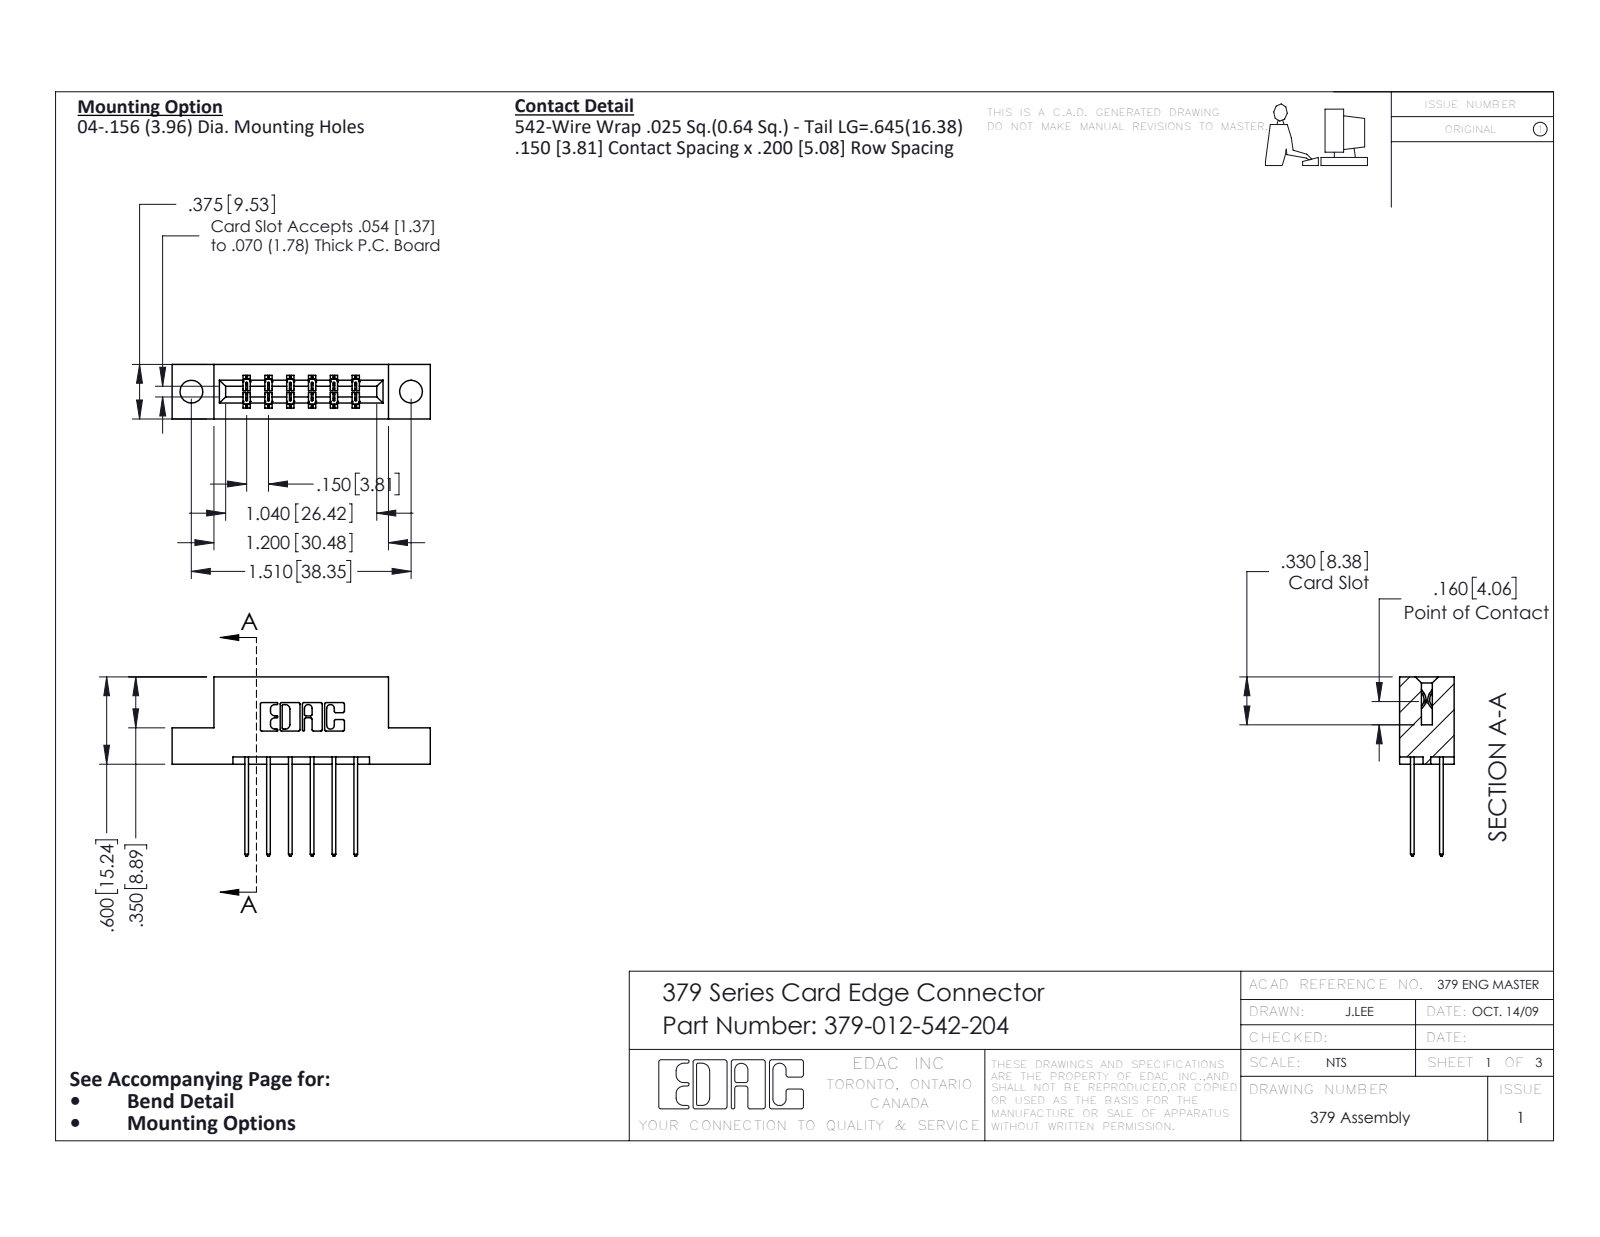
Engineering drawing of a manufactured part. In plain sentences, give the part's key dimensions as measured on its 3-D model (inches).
The part is named "379 Part_Flush - .156 Dia - TH; 379-012-542-204; 345-292-001_345-293-142". Its 3-D file was written by "SolidWorks 2016 (CONFIG_CONTROL_DESIGN)". It is 13 solids with 738 faces: 502 planar, 236 cylindrical and 0 other. Overall it measures 1.775 by 1.232 by 0.375 inches. Its volume is 0.263 cubic inches and its surface area 7.118 square inches. Round holes: 2 of diameter 0.156. Partial cylindrical surfaces (rounded edges, fillets, slot ends): 22 of radius 0.01, 18 of radius 0.006, 12 of radius 0.01, 6 of radius 0.007, 6 of radius 0.031, 3 of radius 0.026, 2 of radius 0.014, 2 of radius 0.022. The main face-to-face distances are 0.3, 0.2, 0.15, 0.1, 0.375, 0.05, 0.075, 0.25, 0.35, 0.55. The hole center spacings are 1.51.
